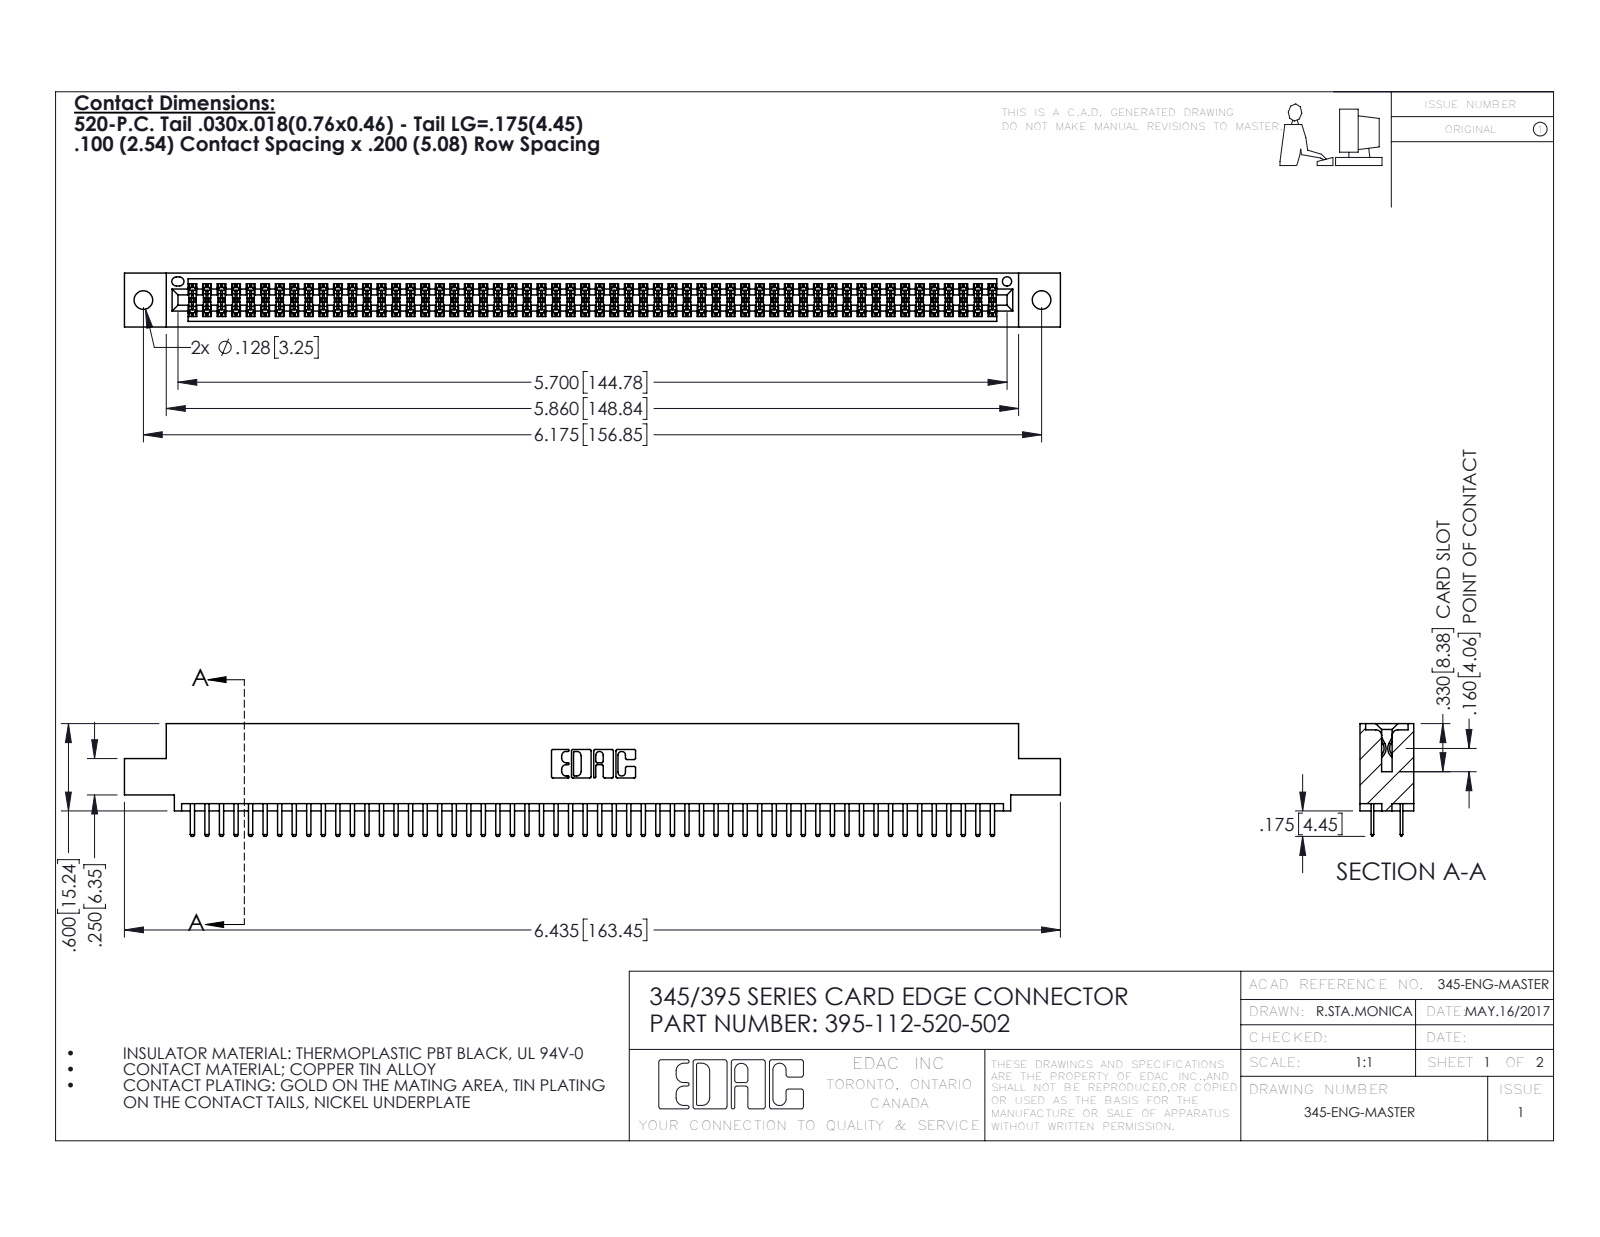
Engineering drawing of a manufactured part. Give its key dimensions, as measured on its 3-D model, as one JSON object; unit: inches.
{"part_name": "395-112-520-502; 345-292-001_345-293-120; 345 Part_0.110 Offset - 0.128 Dia", "step_written_by": "SolidWorks 2016 (CONFIG_CONTROL_DESIGN)", "units": "inches", "bodies": {"solids": 113, "faces": 6178, "planar": 4004, "cylindrical": 2174, "other": 0}, "overall_size": [6.435, 0.775, 0.37], "volume_in3": 0.967, "surface_area_in2": 36.29, "round_holes": [[0.128, 2], [0.064, 1]], "partial_cylinders_radius": [[0.006, 168], [0.01, 116], [0.01, 22], [0.007, 6], [0.031, 6], [0.026, 3], [0.014, 2], [0.019, 2]], "face_to_face_distances": [0.072, 0.298, 0.2, 0.37, 0.098, 0.272, 0.025, 0.225, 0.022, 0.072], "hole_center_spacings": [0.27, 5.939, 6.175]}
